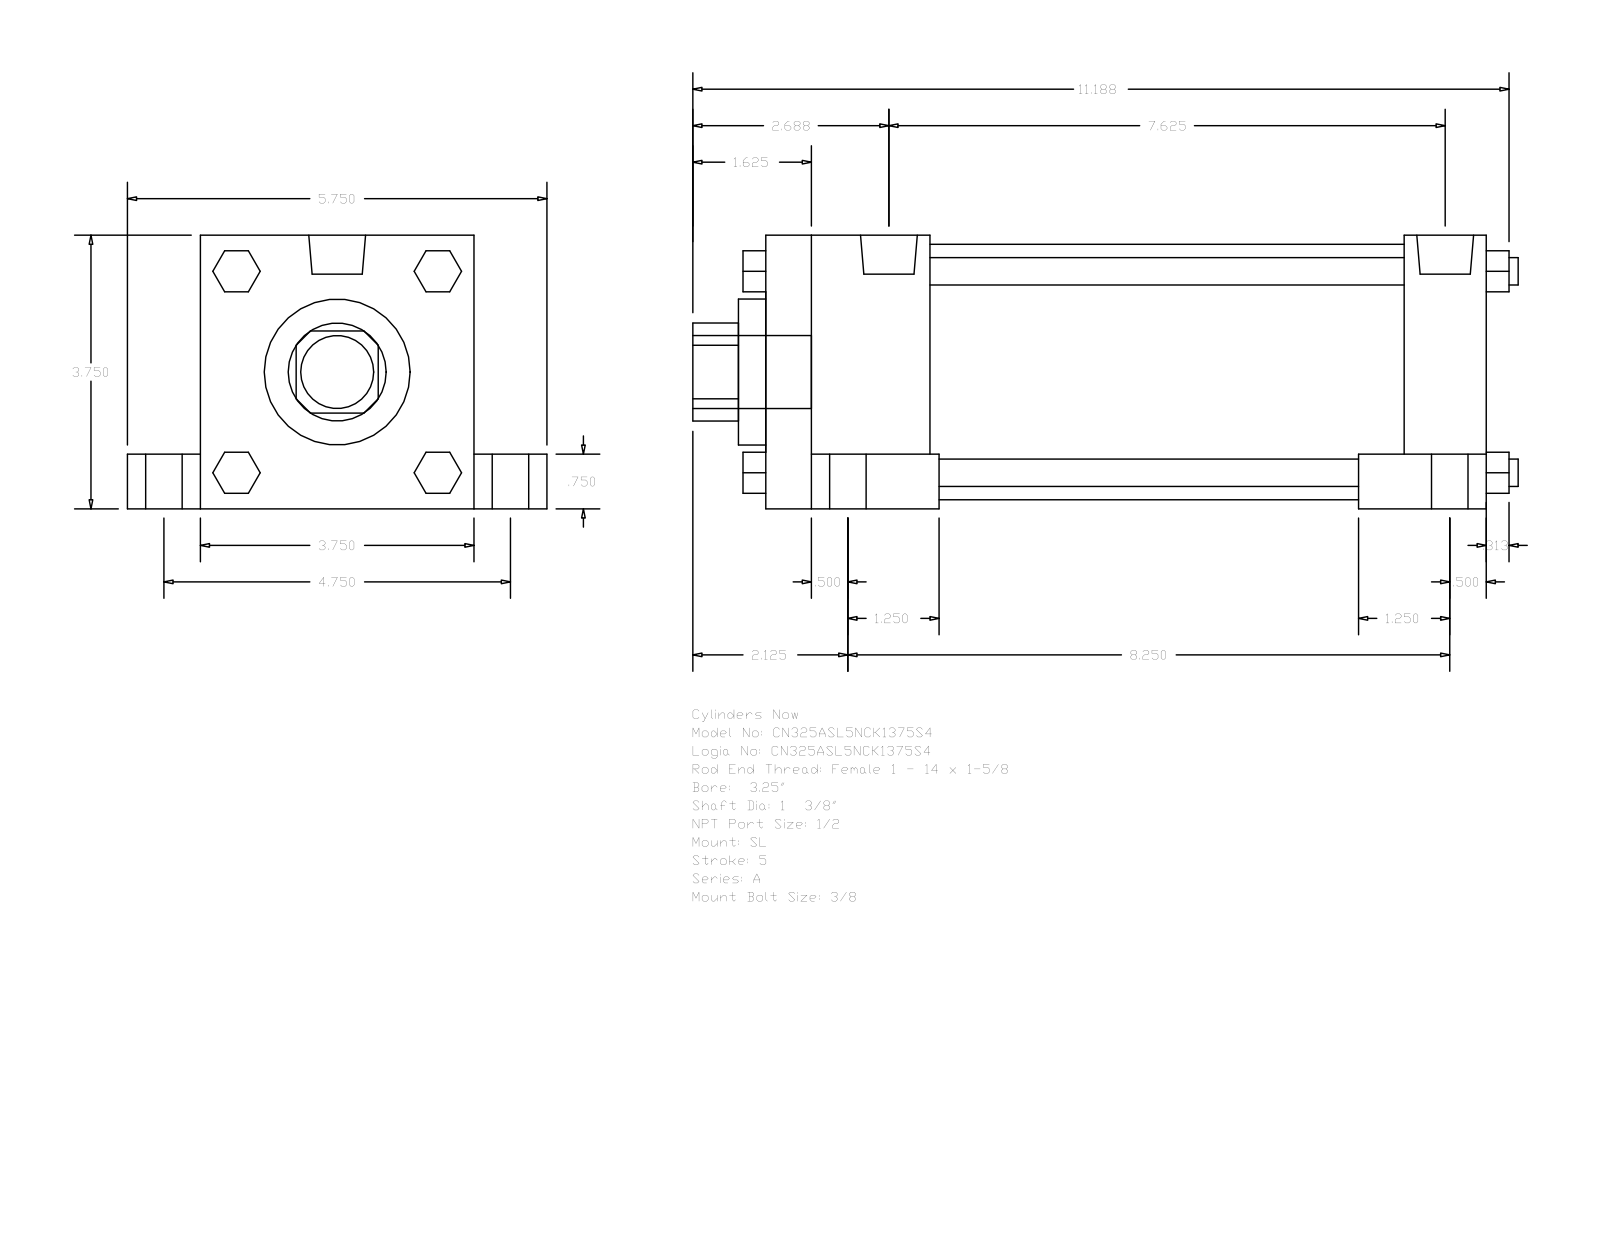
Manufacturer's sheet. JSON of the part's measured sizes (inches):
{"part_name": "A_SL__0325_1.375", "step_written_by": "GSSL Pune (CONFIG_CONTROL_DESIGN)", "units": "inches", "bodies": {"solids": 0, "faces": 150, "planar": 114, "cylindrical": 36, "other": 0}, "overall_size": [11.313, 5.75, 3.75], "round_holes": [[1.375, 1], [2, 1], [3.5, 1]], "round_bosses_or_shafts": [[0.75, 4], [0.5, 4], [0.375, 4], [0.344, 4], [0.778, 2], [1, 1]], "partial_cylinders_radius": [[0.672, 1]], "face_to_face_distances": [3.75, 9.875, 1, 4.75, 0.75, 3, 0.625, 1.125, 5.75, 2.25]}
